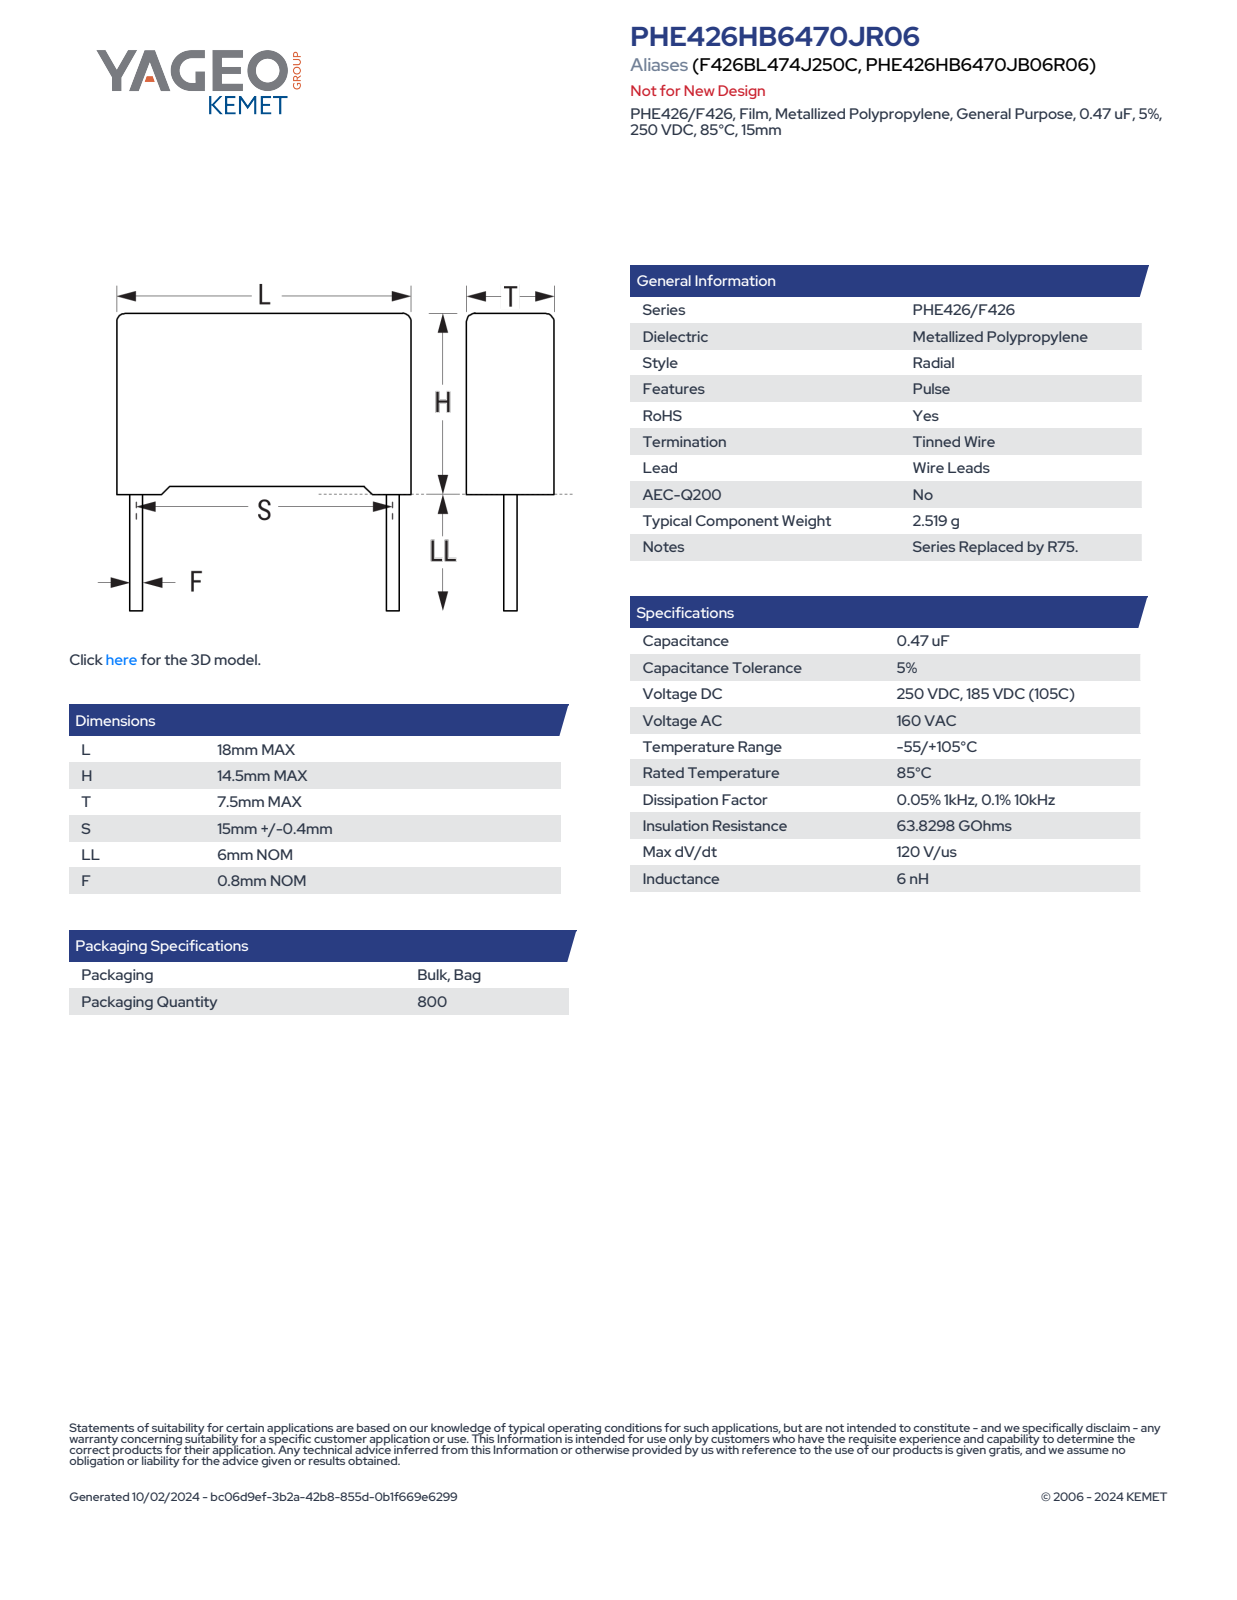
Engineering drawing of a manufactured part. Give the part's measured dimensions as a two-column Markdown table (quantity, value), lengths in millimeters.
| quantity | value |
| --- | --- |
| part name | CFR_RB2_18X14.5X7.5_L18H14.5T7.5S15LL6F0.8 |
| STEP written by | SolidWorks 2021 (AUTOMOTIVE_DESIGN) |
| units | millimeters |
| bodies | 4 solids, 85 faces (77 planar, 8 cylindrical, 0 other) |
| overall size | 20.5 × 18 × 7.5 |
| volume | 1 875 mm³ |
| surface area | 1 069 mm² |
| round bosses / shafts (diameter × count) | 0.8 × 2 |
| partial cylindrical surfaces (radius × count) | 0.5 × 4 |
| main face-to-face distances | 7.5, 18, 13.75, 0.6, 0.75, 14.5, 6.9, 0.5, 14, 17.4 |
